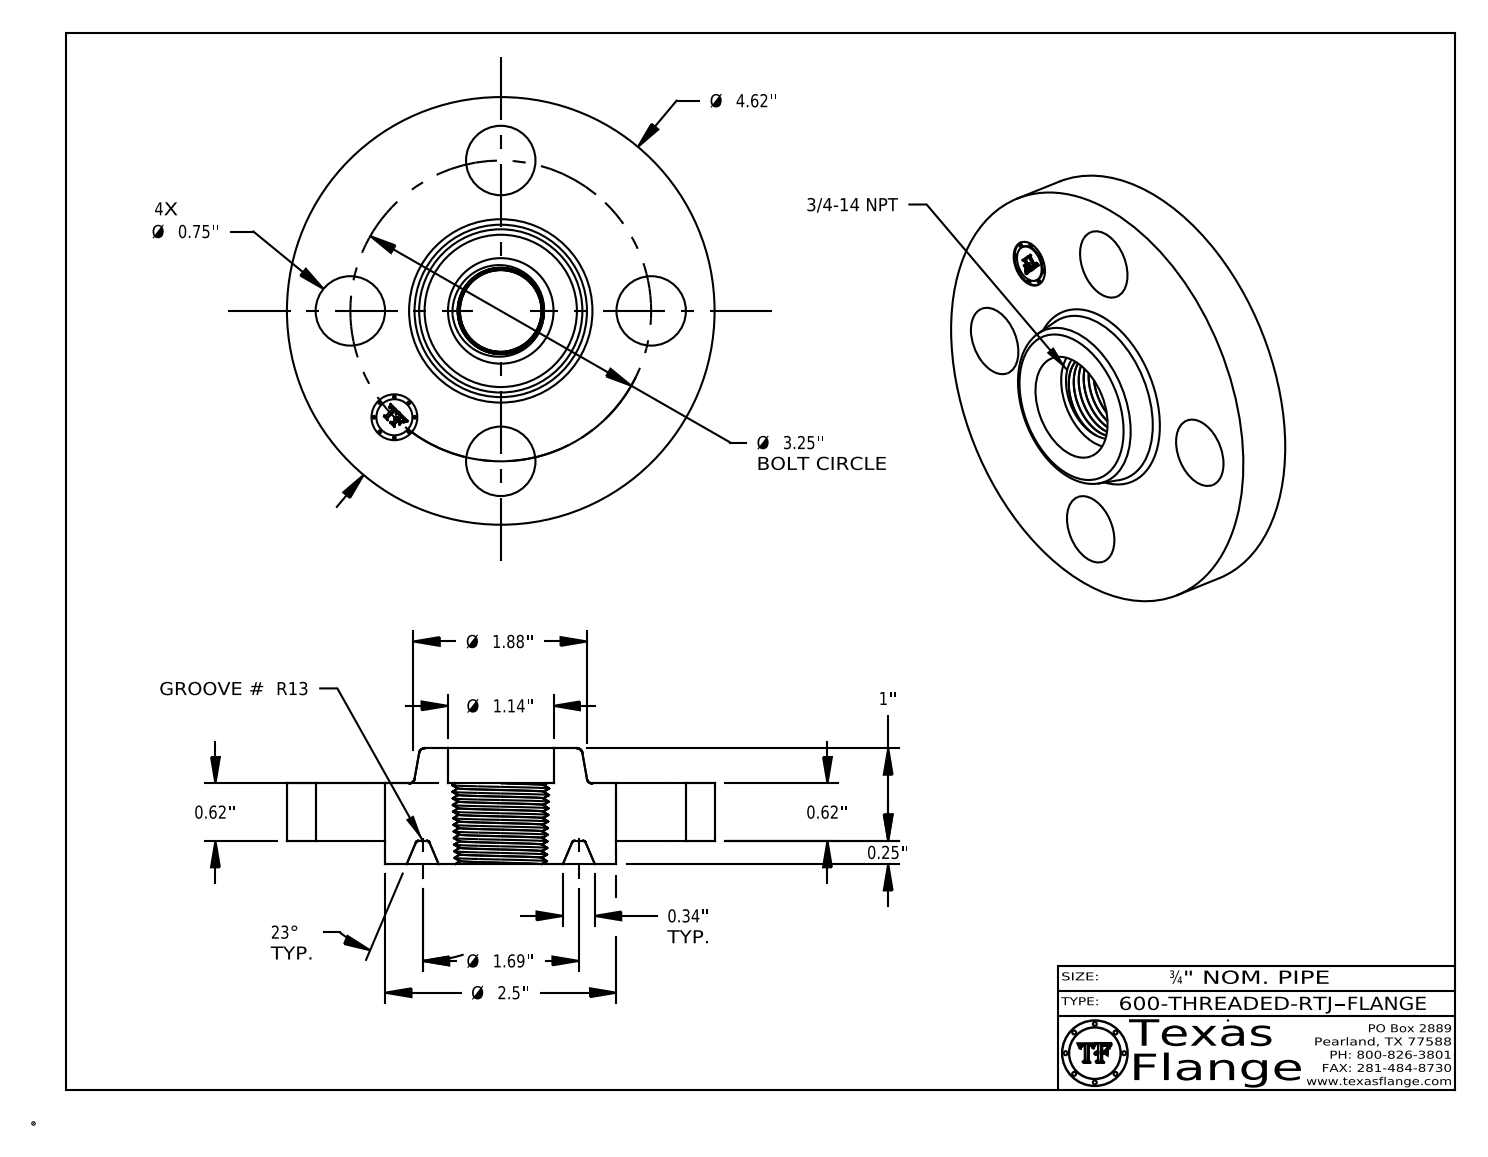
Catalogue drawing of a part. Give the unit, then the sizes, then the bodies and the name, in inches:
Units: inches
Overall size (bounding box): 4.62 × 4.62 × 1.25
Round holes (diameter × count): ⌀0.75 ×4, ⌀0.495 ×1, ⌀1.14 ×1
Round bosses / shafts (diameter × count): ⌀0.03 ×8, ⌀4.62 ×1, ⌀2.5 ×1, ⌀0.39 ×1
Main face-to-face distances: 0.62, 0.25, 0.87, 1.25, 1, 0.38, 0.855, 0.605, 0.015, 0.395
Hole centre spacings: 1.625, 2.298, 1.244, 3.003, 3.25
Volume: 10.17 in³ · Surface area: 55.03 in²
Bodies: 1 solid, 548 faces (372 planar, 34 cylindrical, 142 other)
Part name (STEP PRODUCT): 600-THREADED-RTJ
STEP written by: CATIA V5 STEP AP214 (AUTOMOTIVE_DESIGN)
